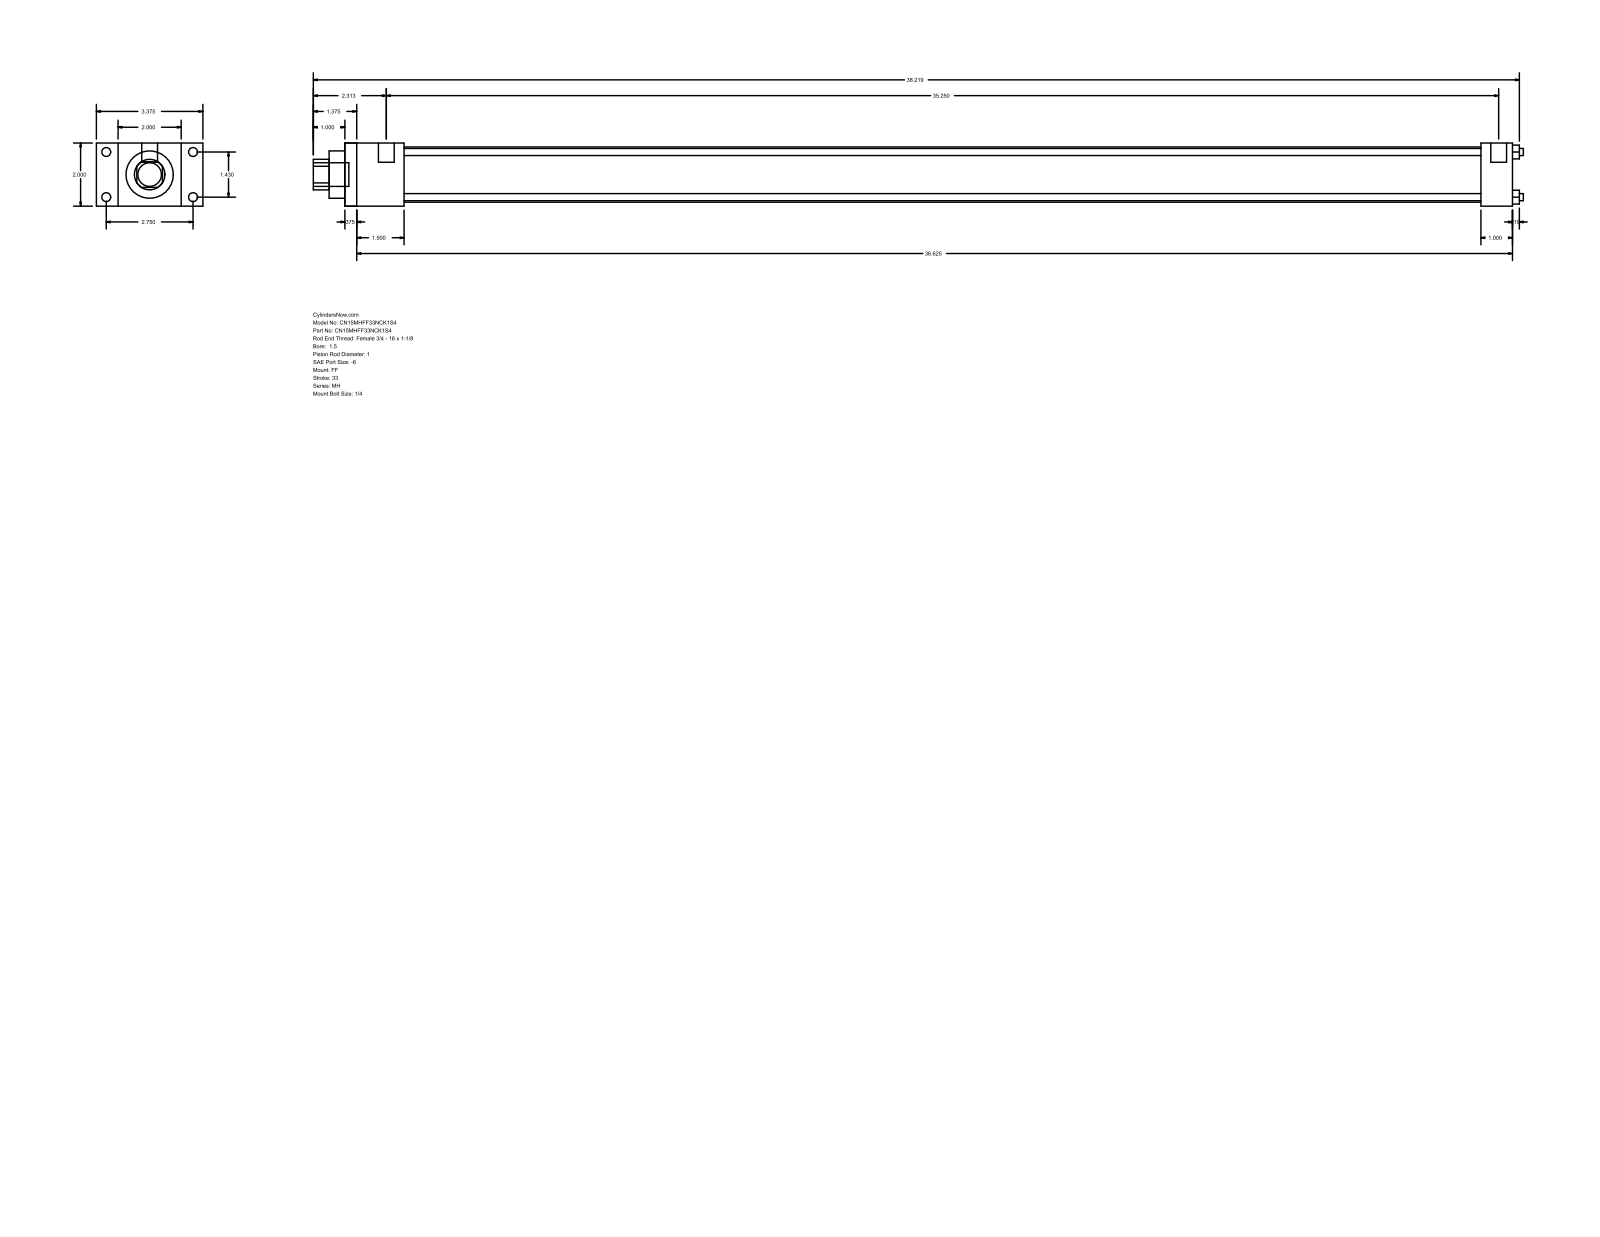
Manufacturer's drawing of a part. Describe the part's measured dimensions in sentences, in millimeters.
The part is named "MH_FF__0150_1". Its 3-D file was written by "GSSL Pune (CONFIG_CONTROL_DESIGN)". It is 0 solids with 92 faces: 64 planar, 28 cylindrical and 0 other. Overall it measures 973.93 by 85.72 by 50.8 millimeters. Round holes: 4 of diameter 5.71, 1 of diameter 25.4, 1 of diameter 38.1, 1 of diameter 44.45. Round bosses or shafts: 4 of diameter 7.14, 4 of diameter 5.56, 2 of diameter 12.7, 1 of diameter 19.05. Partial cylindrical surfaces (rounded edges, fillets, slot ends): 1 of radius 12.29. The main face-to-face distances are 50.8, 939.8, 9.52, 930.28, 25.4, 17.46, 68.26, 47.63, 38.11, 892.17. The hole center spacings are 25.68, 36.32, 51.36.
